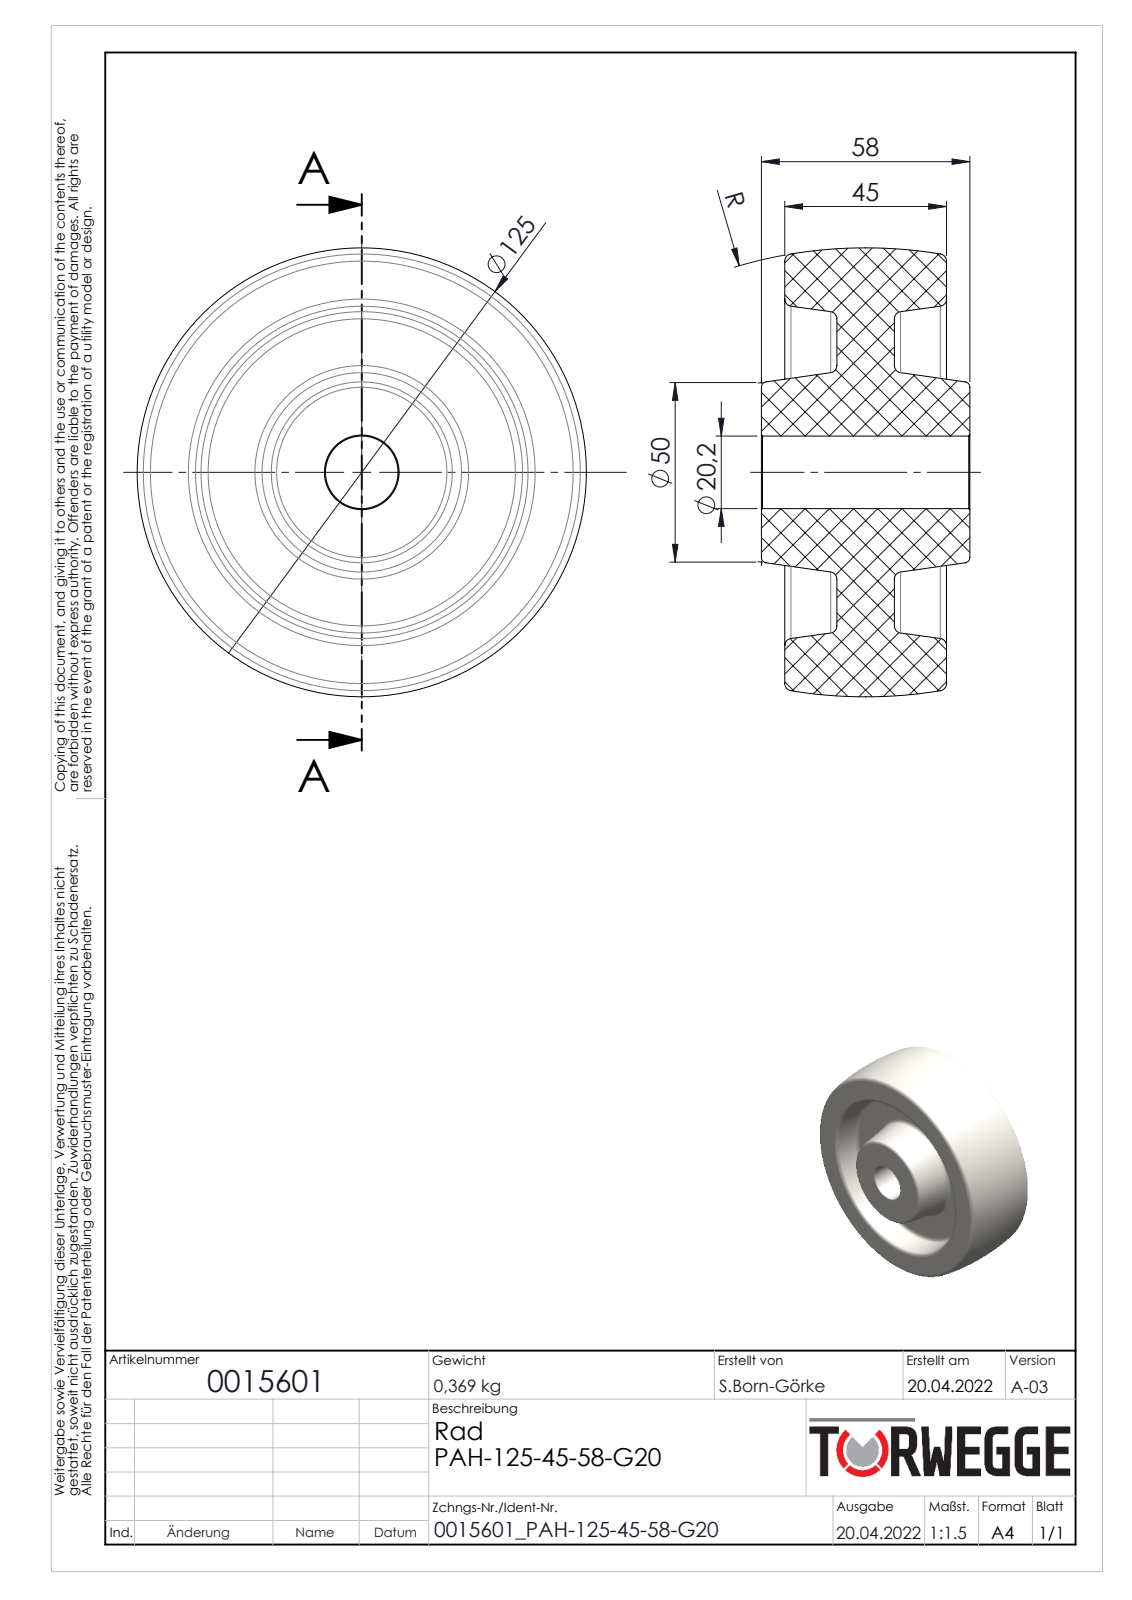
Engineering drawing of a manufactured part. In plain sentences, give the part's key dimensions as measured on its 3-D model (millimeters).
The part is named "0015601". Its 3-D file was written by "SolidWorks 2020 (AUTOMOTIVE_DESIGN)". It is 1 solid with 44 faces: 6 planar, 2 cylindrical and 36 other. Overall it measures 125 by 125 by 58 millimeters. Its volume is 425 904 cubic millimeters and its surface area 55 385 square millimeters. Round holes: 1 of diameter 20.2. The main face-to-face distances are 14.5, 30.5, 45, 16, 6.5, 21, 37, 51.5, 58.
